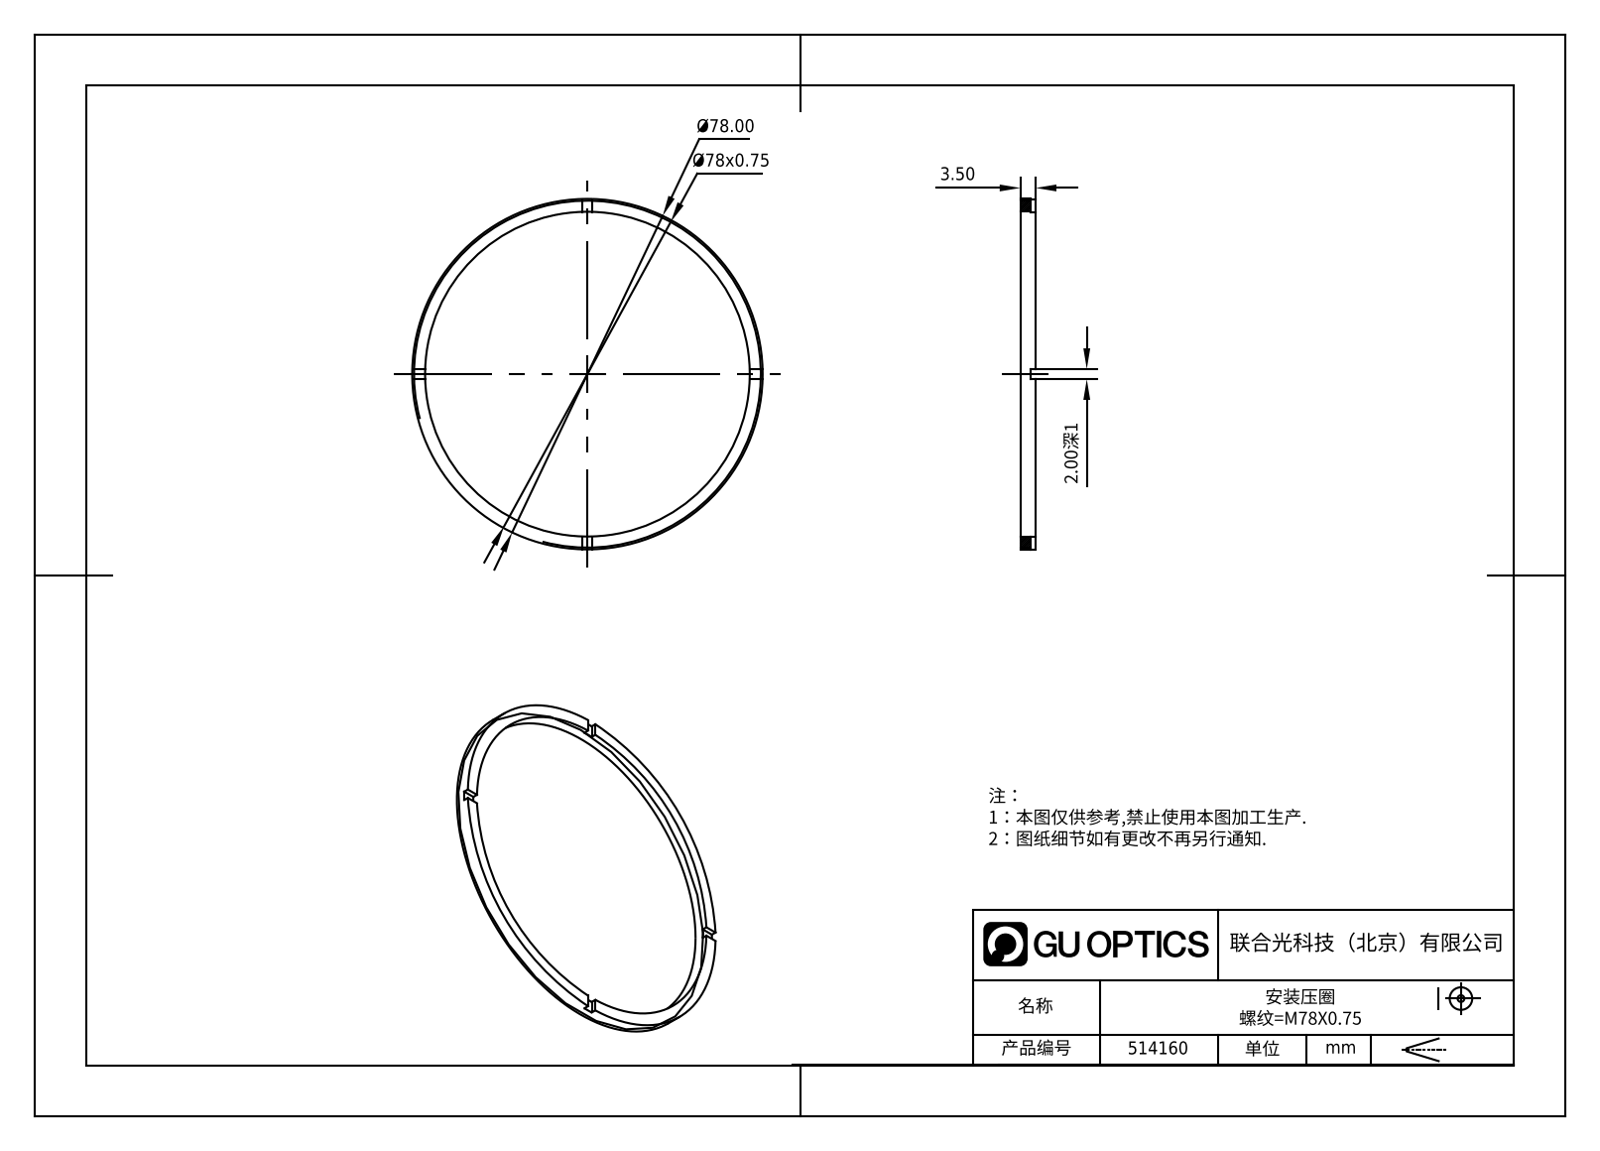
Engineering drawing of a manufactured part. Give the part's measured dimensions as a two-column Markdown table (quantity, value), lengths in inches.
| quantity | value |
| --- | --- |
| part name | 514160 |
| STEP written by | SolidWorks 2020 (CONFIG_CONTROL_DESIGN) |
| units | inches |
| bodies | 1 solid, 21 faces (17 planar, 4 cylindrical, 0 other) |
| overall size | 3.071 × 3.071 × 0.138 |
| volume | 0.15 in³ |
| surface area | 4.76 in² |
| round holes (diameter × count) | 2.835 × 1 |
| round bosses / shafts (diameter × count) | 3.071 × 1 |
| main face-to-face distances | 0.138, 0.098, 0.039, 0.079 |
